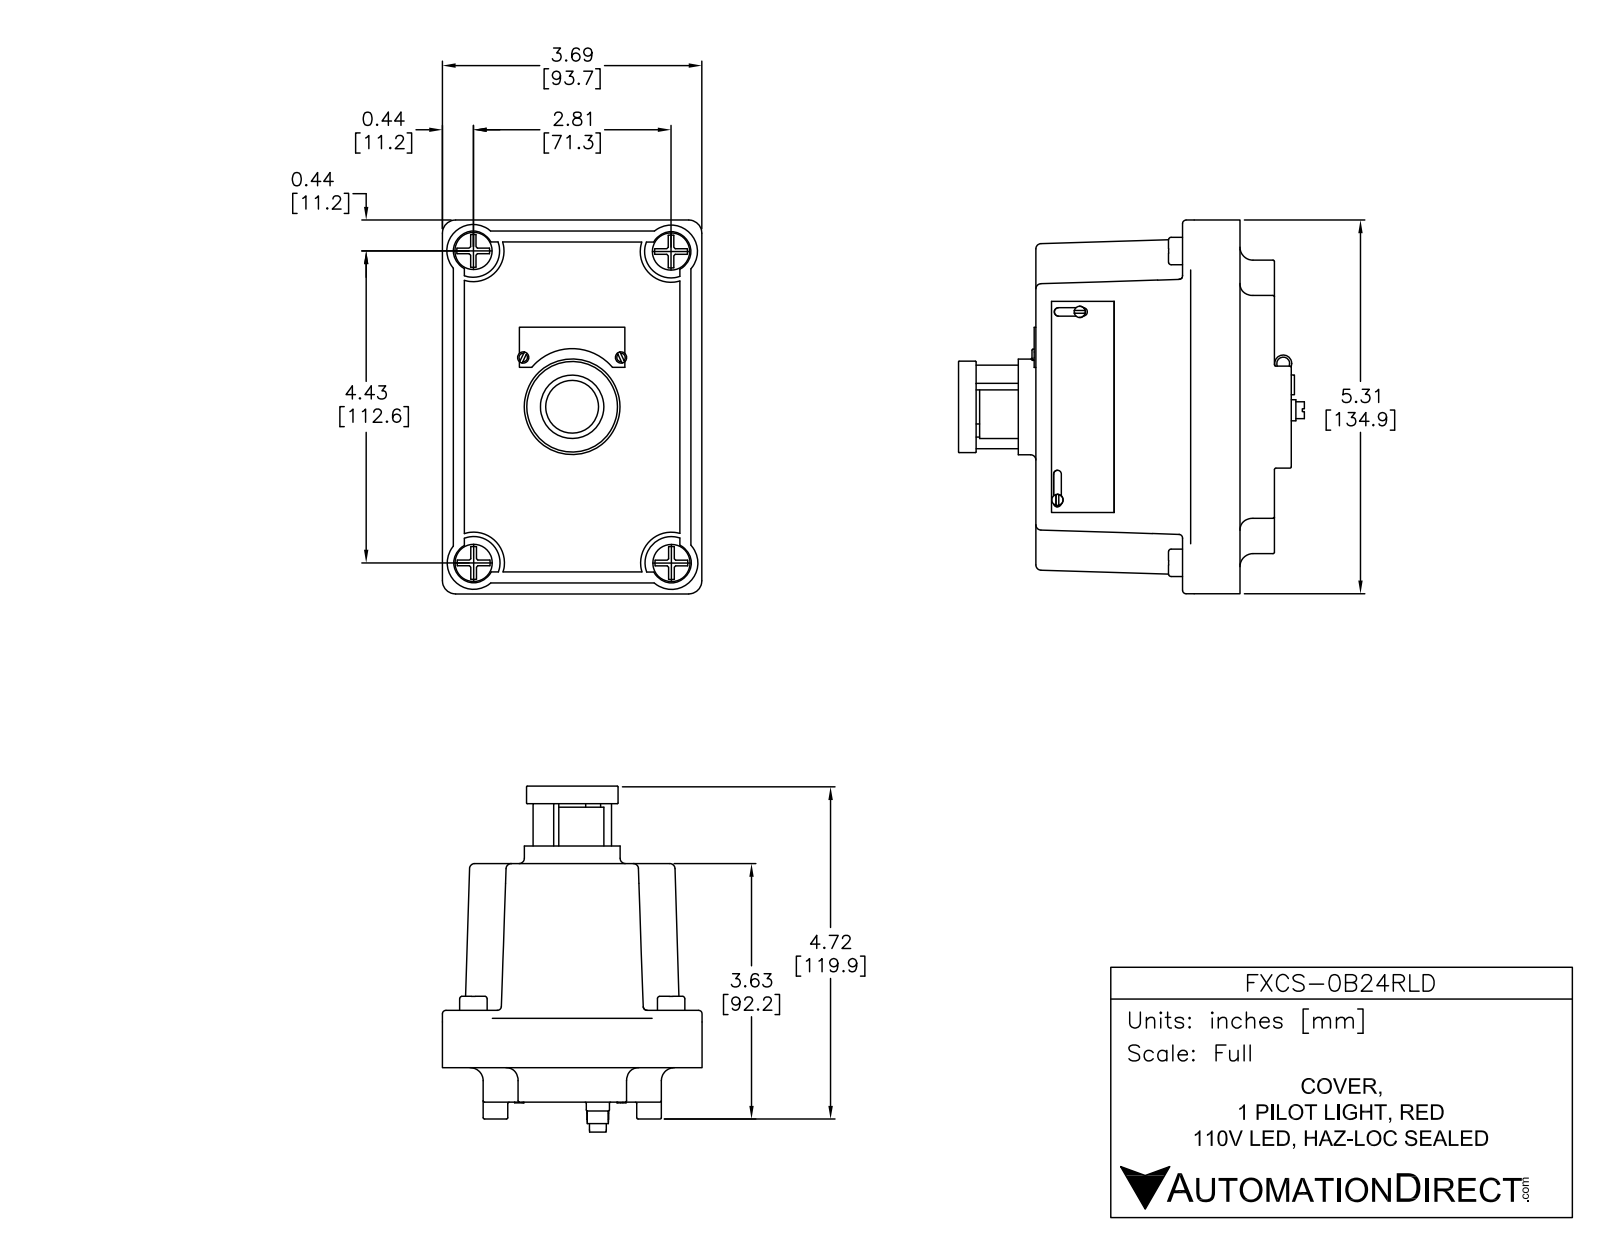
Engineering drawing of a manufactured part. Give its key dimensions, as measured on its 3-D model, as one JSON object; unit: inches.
{"part_name": "FXCS-0B24RLD", "step_written_by": "SolidWorks 2015 (AUTOMOTIVE_DESIGN)", "units": "inches", "bodies": {"solids": 1, "faces": 696, "planar": 288, "cylindrical": 147, "other": 261}, "overall_size": [5.31, 4.989, 3.69], "volume_in3": 48.88, "surface_area_in2": 99.55, "round_holes": [[0.16, 8], [0.198, 1], [0.94, 1]], "round_bosses_or_shafts": [[0.16, 6], [0.39, 4], [1.36, 1], [1.3, 1], [0.9, 1], [0.33, 1], [0.3, 1], [0.24, 1]], "partial_cylinders_radius": [[0.02, 22], [0.05, 12], [0.055, 4], [0.06, 4], [0.075, 4], [0.185, 4], [0.42, 4], [0.653, 3]], "face_to_face_distances": [3.39, 0.49, 2.9, 0.02, 3.69, 0.578, 3.111, 1.19, 0.7, 2.2], "hole_center_spacings": [0.25, 2.197, 0.5, 2.183, 2.239, 0.75, 1.092, 1.115]}
